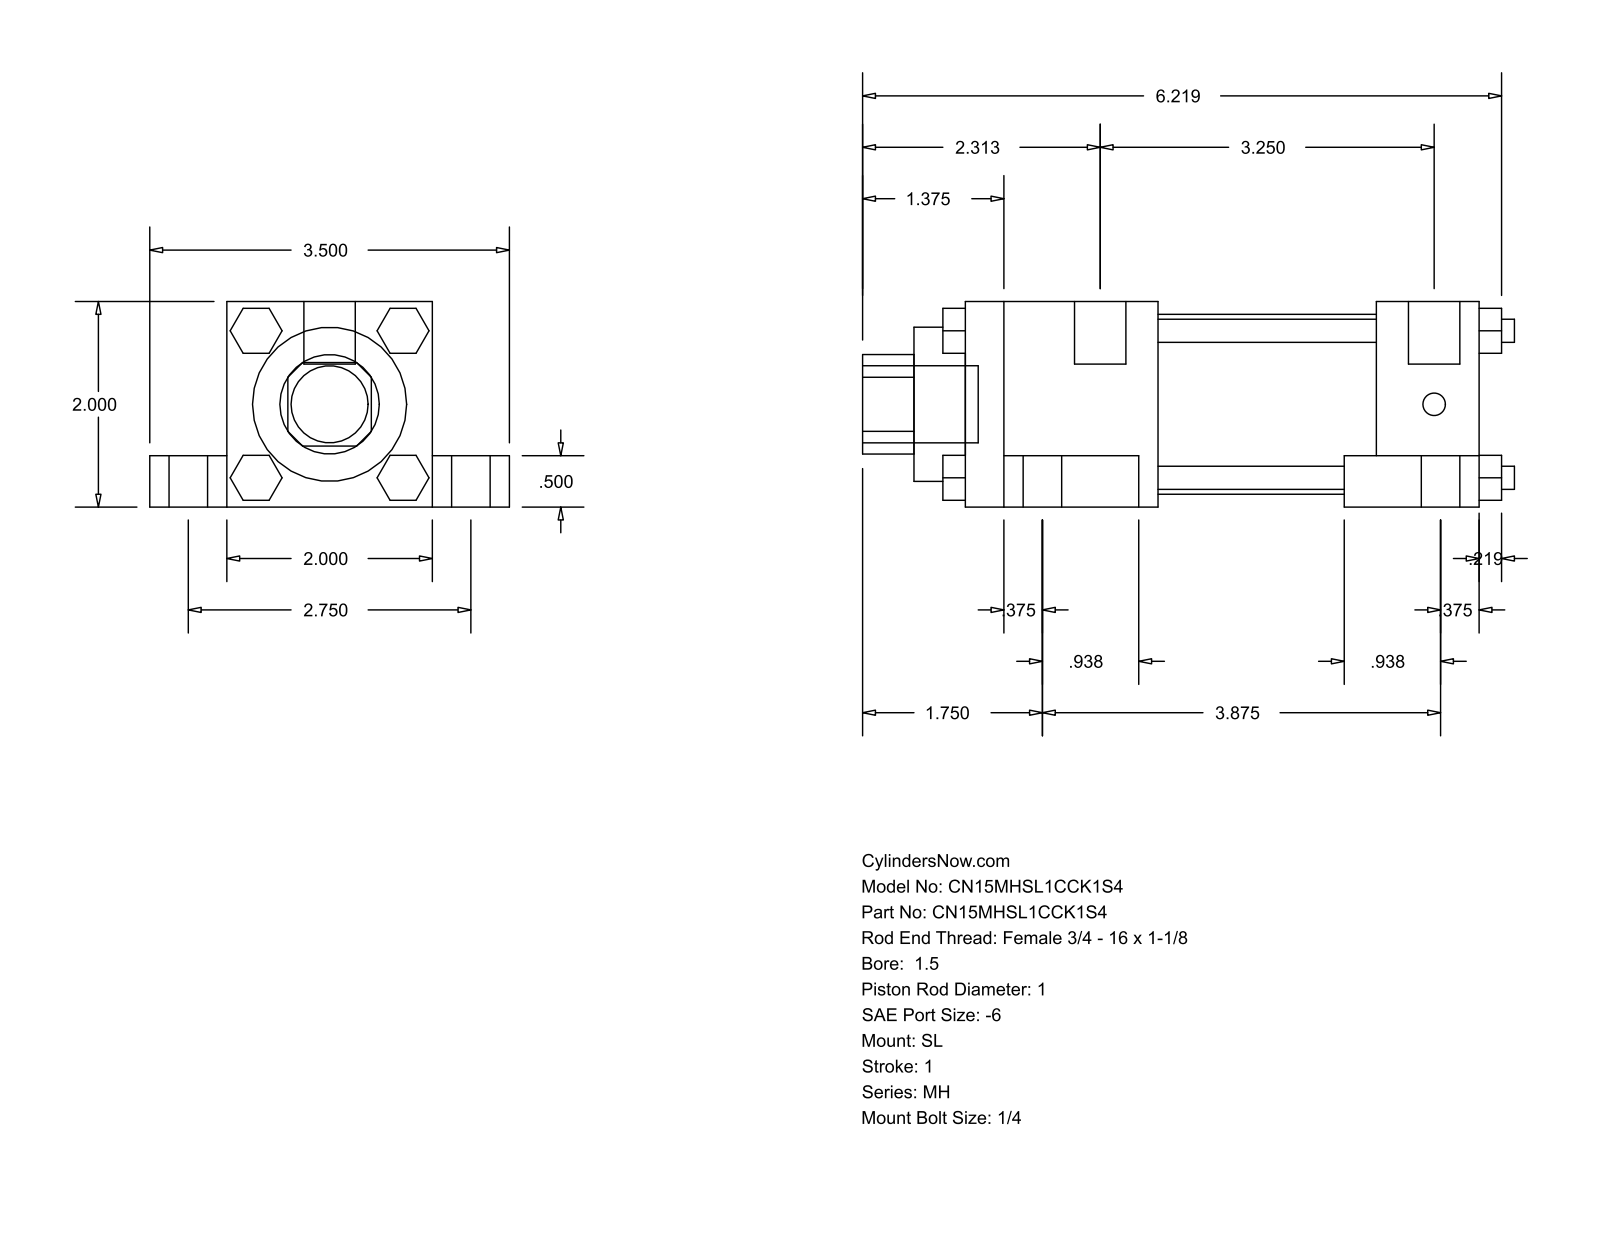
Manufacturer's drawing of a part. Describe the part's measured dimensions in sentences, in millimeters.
The part is named "MH_SL__0150_1". Its 3-D file was written by "GSSL Pune (CONFIG_CONTROL_DESIGN)". It is 0 solids with 148 faces: 112 planar, 36 cylindrical and 0 other. Overall it measures 161.13 by 88.9 by 50.8 millimeters. Round holes: 1 of diameter 25.4, 1 of diameter 38.1, 1 of diameter 44.45. Round bosses or shafts: 4 of diameter 15.88, 4 of diameter 9.53, 4 of diameter 5.71, 4 of diameter 5.56, 2 of diameter 12.7, 1 of diameter 19.05. Partial cylindrical surfaces (rounded edges, fillets, slot ends): 1 of radius 12.29. The main face-to-face distances are 50.8, 12.7, 38.1, 19.05, 69.85, 127, 25.4, 9.52, 33.34, 84.14.
